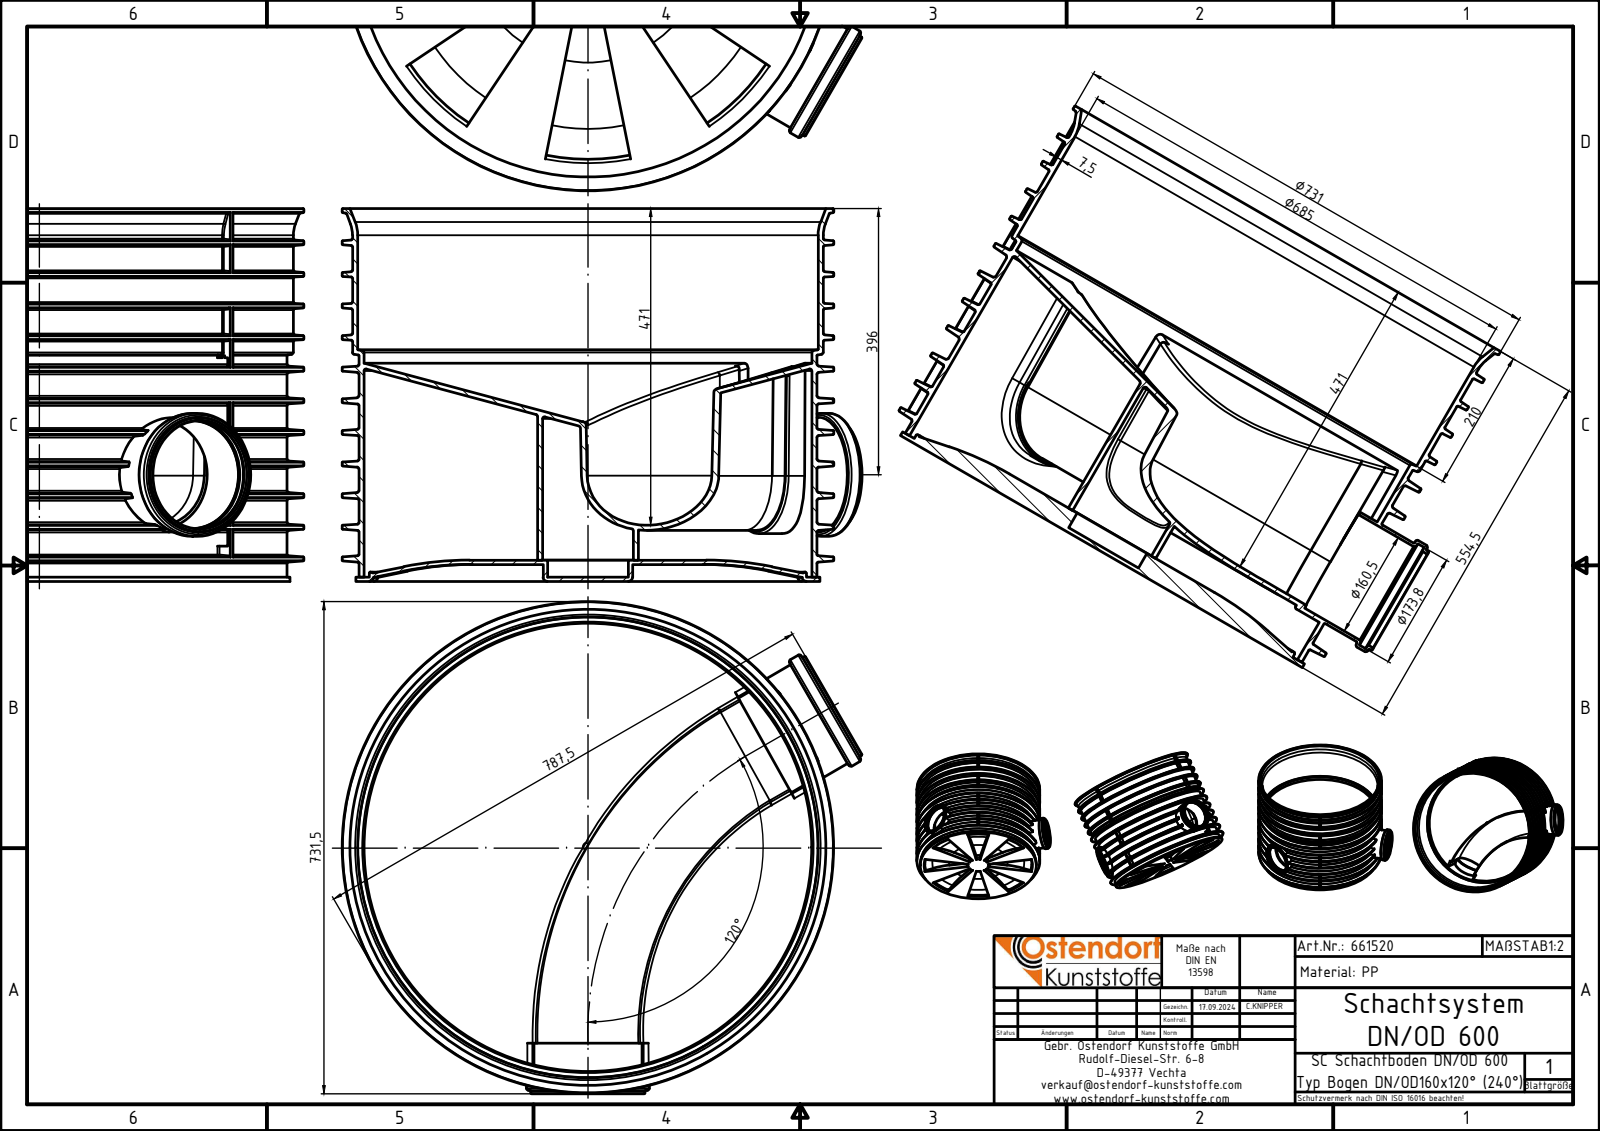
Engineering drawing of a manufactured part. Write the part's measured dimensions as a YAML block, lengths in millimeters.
part_name: "661520z; 661520 Schacht DN600 Boden; 661520 Schachtboden DN600 Grundkörper"
step_written_by: "Autodesk Inventor 2024 (AUTOMOTIVE_DESIGN)"
units: millimeters
bodies: {solids: 2, faces: 1523, planar: 157, cylindrical: 256, other: 1110}
overall_size: [773.05, 731.5, 554.5]
volume: 23320000
surface_area: 5540000
round_holes:
  - {diameter: 160.5, count: 2}
  - {diameter: 160.8, count: 2}
  - {diameter: 173.8, count: 2}
  - {diameter: 120, count: 1}
  - {diameter: 135, count: 1}
  - {diameter: 160.7, count: 1}
  - {diameter: 169.8, count: 1}
  - {diameter: 640, count: 1}
  - {diameter: 666, count: 1}
  - {diameter: 685, count: 1}
round_bosses_or_shafts:
  - {diameter: 182.8, count: 2}
  - {diameter: 169.5, count: 2}
  - {diameter: 731, count: 1}
  - {diameter: 700, count: 1}
  - {diameter: 690, count: 1}
  - {diameter: 681, count: 1}
  - {diameter: 650, count: 1}
  - {diameter: 169.8, count: 1}
partial_cylinders:
  - {radius: 2, count: 16}
  - {radius: 1, count: 8}
  - {radius: 3, count: 4}
  - {radius: 87.5, count: 2}
  - {radius: 66.5, count: 1}
  - {radius: 318.5, count: 1}
  - {radius: 360, count: 1}
face_to_face_distances: [6.5, 25, 31.5, 18.5, 554.5, 548, 529.5, 523, 7.5, 14]
